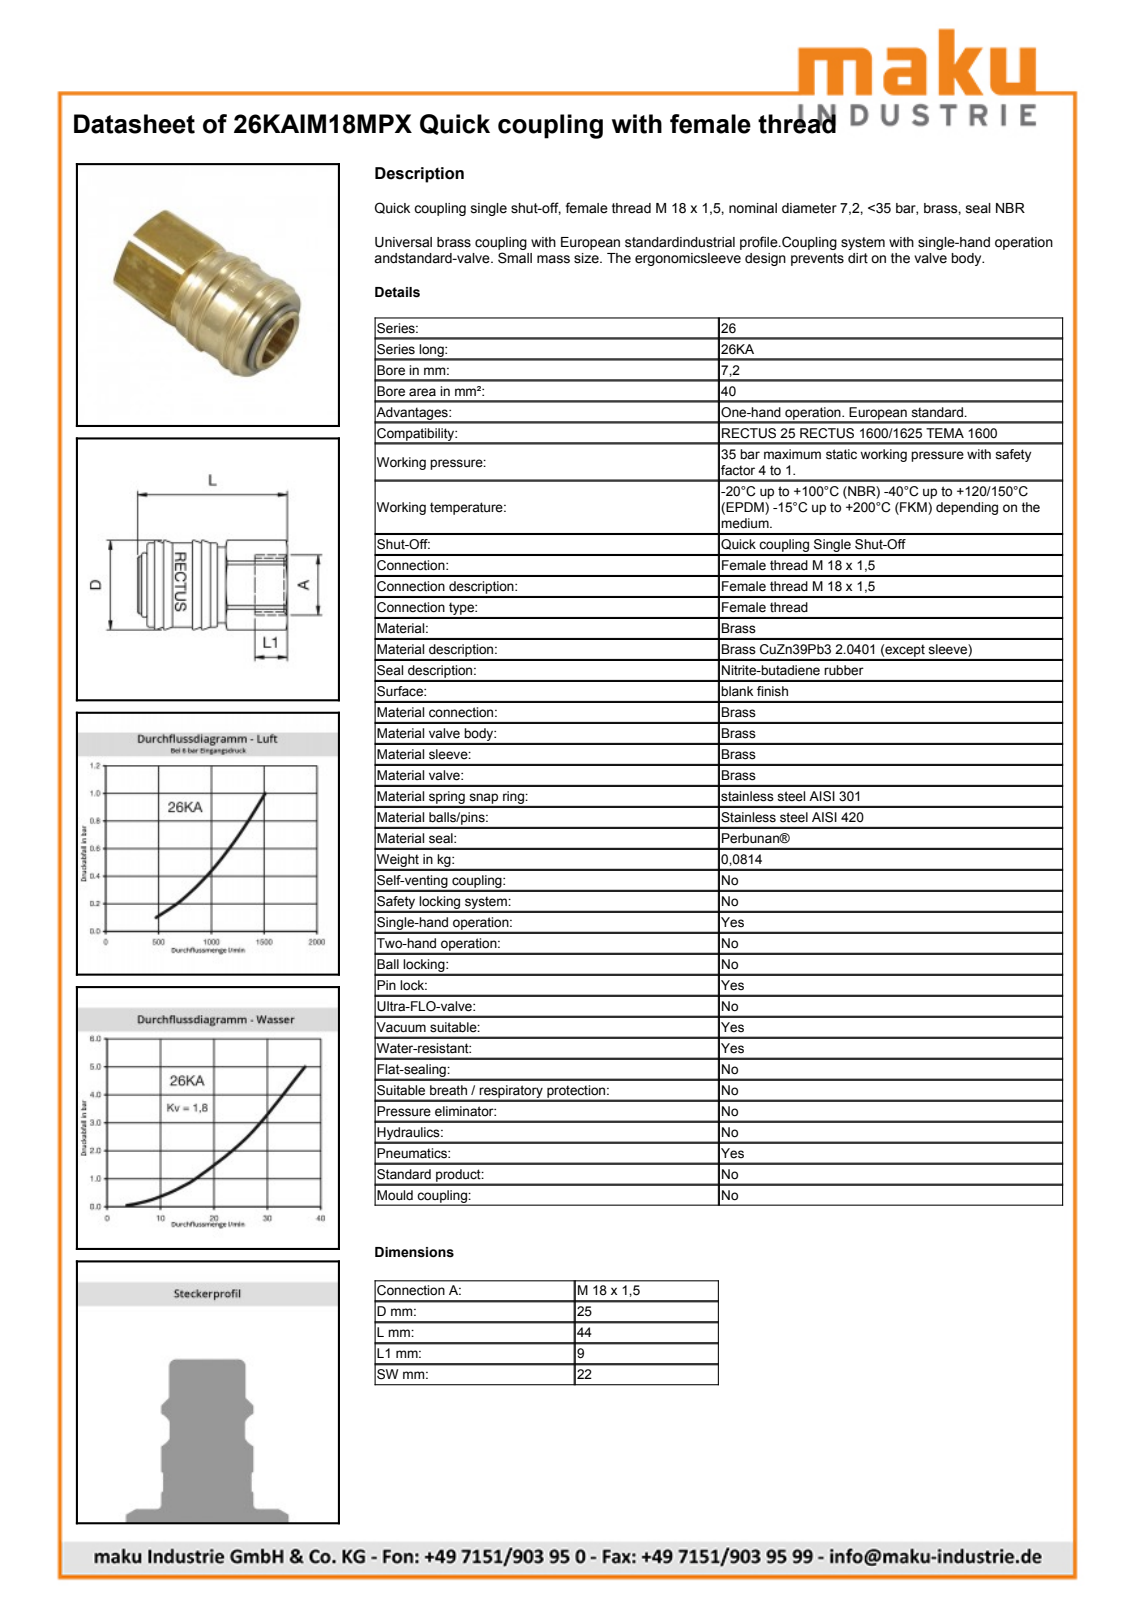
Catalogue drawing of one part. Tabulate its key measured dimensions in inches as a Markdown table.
| quantity | value |
| --- | --- |
| part name | D103031 |
| STEP written by | Autodesk Inventor 2011 (AUTOMOTIVE_DESIGN) |
| units | inches |
| bodies | 3 solids, 636 faces (241 planar, 72 cylindrical, 323 other) |
| overall size | 1.614 × 0.976 × 0.976 |
| volume | 0.782 in³ |
| surface area | 13.88 in² |
| round holes (diameter × count) | 0.569 × 1, 0.573 × 1, 0.608 × 1, 0.634 × 1, 0.66 × 1, 0.675 × 1, 0.831 × 1 |
| round bosses / shafts (diameter × count) | 0.917 × 1, 0.827 × 1, 0.709 × 1, 0.656 × 1, 0.628 × 1, 0.589 × 1, 0.545 × 1 |
| partial cylindrical surfaces (radius × count) | 0.455 × 1, 0.488 × 1 |
| main face-to-face distances | 0.866, 1.156, 0.104, 1.26, 0.354, 1.614, 1.51, 0.827, 0.433, 0.722 |
